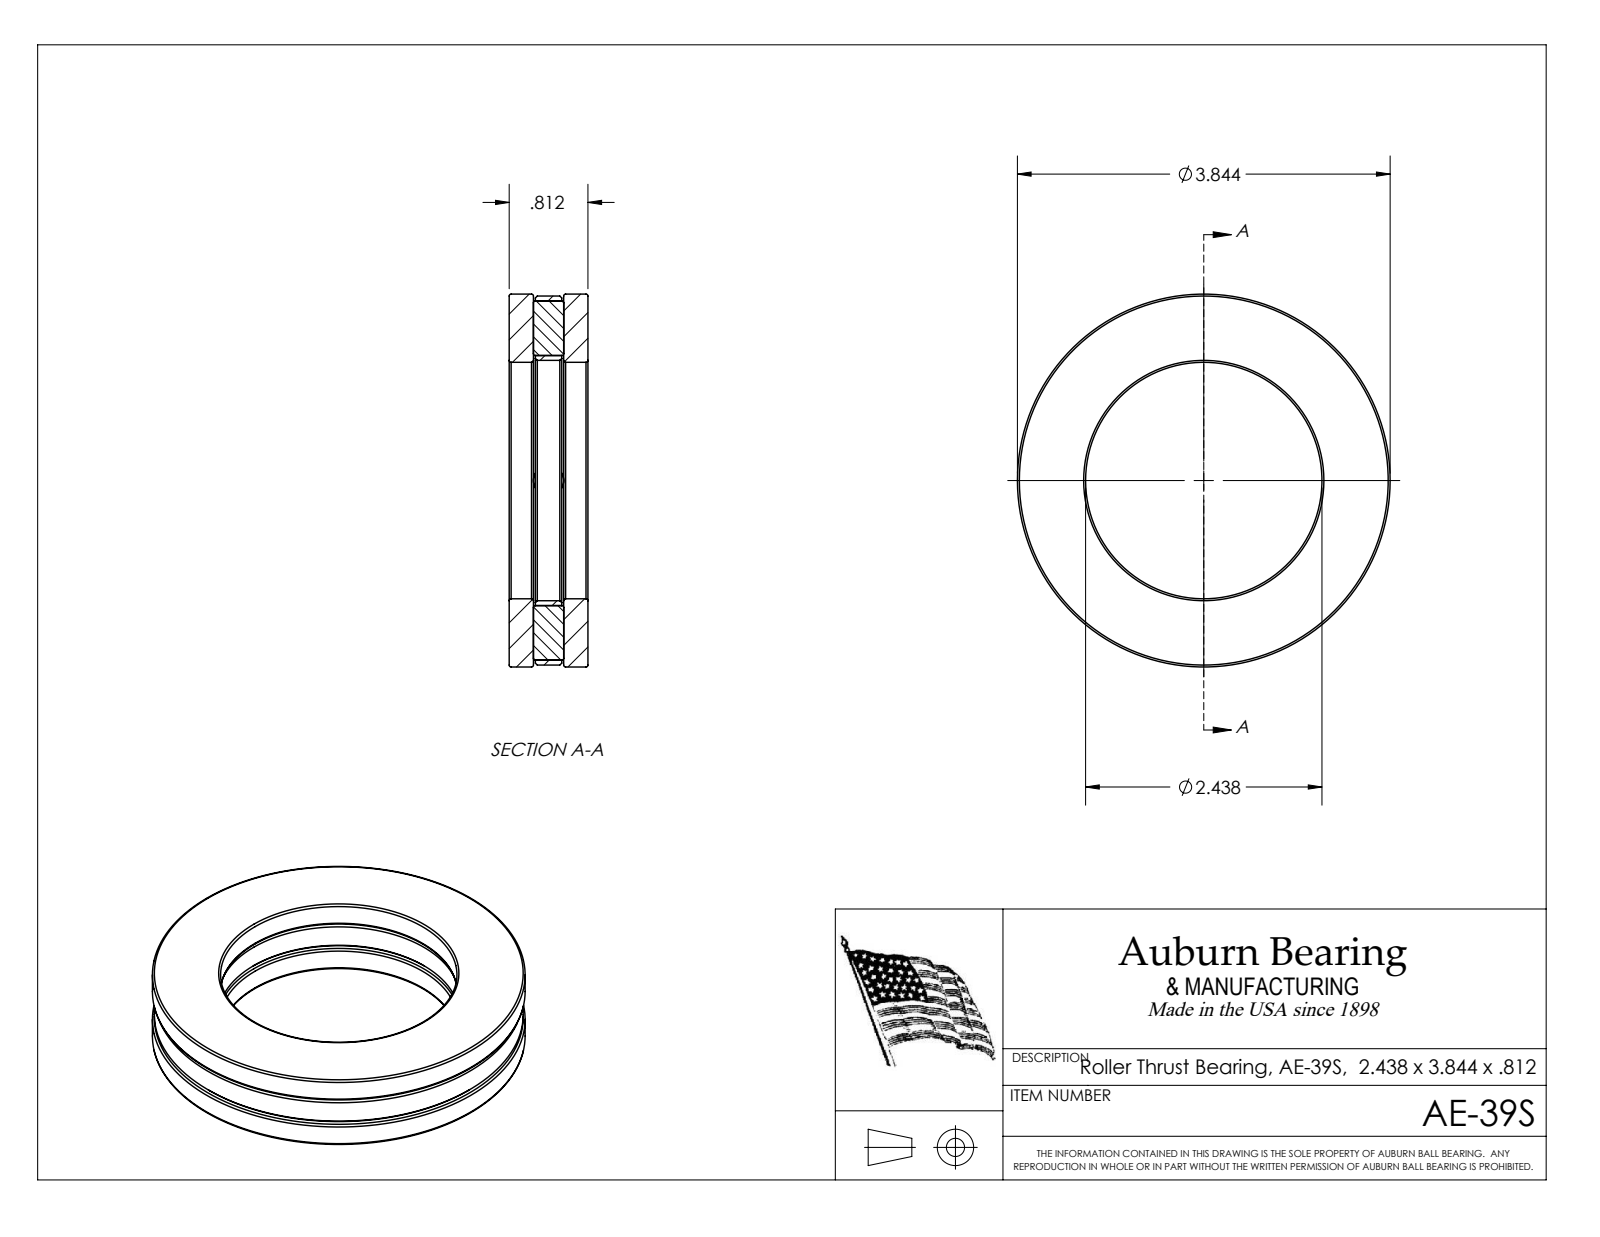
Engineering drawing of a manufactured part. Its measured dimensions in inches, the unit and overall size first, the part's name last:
Units: inches
Overall size (bounding box): 3.844 × 3.844 × 0.812
Round holes (diameter × count): ⌀2.437 ×1, ⌀2.477 ×1
Round bosses / shafts (diameter × count): ⌀0.312 ×2, ⌀3.844 ×1, ⌀3.804 ×1
Main face-to-face distances: 0.25, 0.562, 0.27, 0.542, 0.02, 0.292, 0.312, 0.812, 0.272, 1.133
Volume: 5.214 in³ · Surface area: 58.18 in²
Bodies: 7 solids, 60 faces (30 planar, 10 cylindrical, 20 other)
Part name (STEP PRODUCT): AE-39S
STEP written by: SolidWorks 2017 (CONFIG_CONTROL_DESIGN)
